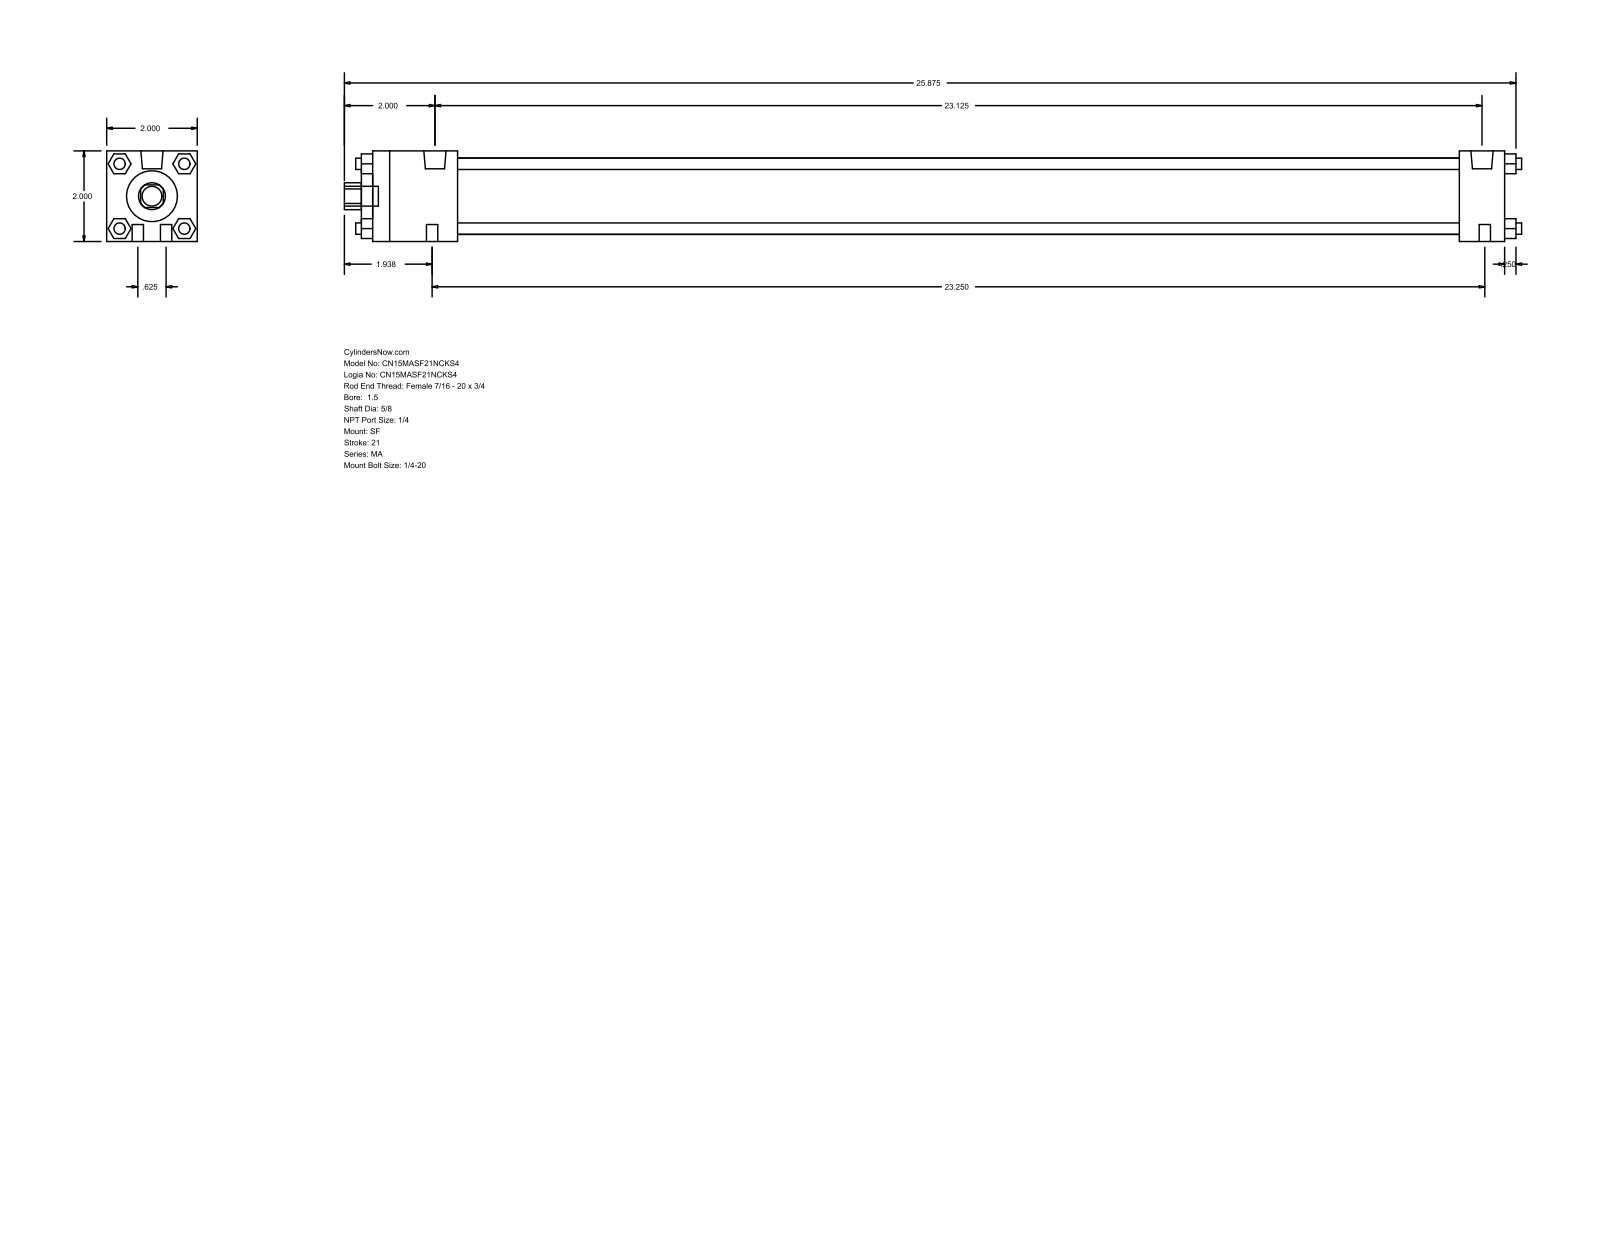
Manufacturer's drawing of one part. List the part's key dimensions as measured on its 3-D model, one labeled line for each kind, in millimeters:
Part name (STEP PRODUCT): MA_SF__0150_0.625
STEP written by: GSSL Pune (CONFIG_CONTROL_DESIGN)
Units: millimetres
Bodies: 0 solids, 124 faces (94 planar, 30 cylindrical, 0 other)
Overall size (bounding box): 660.4 × 50.8 × 50.8
Round holes (diameter × count): ⌀15.88 ×1, ⌀28.57 ×1, ⌀42.93 ×1
Round bosses / shafts (diameter × count): ⌀6.35 ×8, ⌀12.49 ×2, ⌀7.94 ×2, ⌀11.11 ×1
Partial cylindrical surfaces — rounded edges, fillets, slot ends (radius × count): R7.54 ×1
Main face-to-face distances: 50.8, 635, 6.35, 641.35, 47.62, 609.6, 561.98, 587.38, 25.4, 53.97
